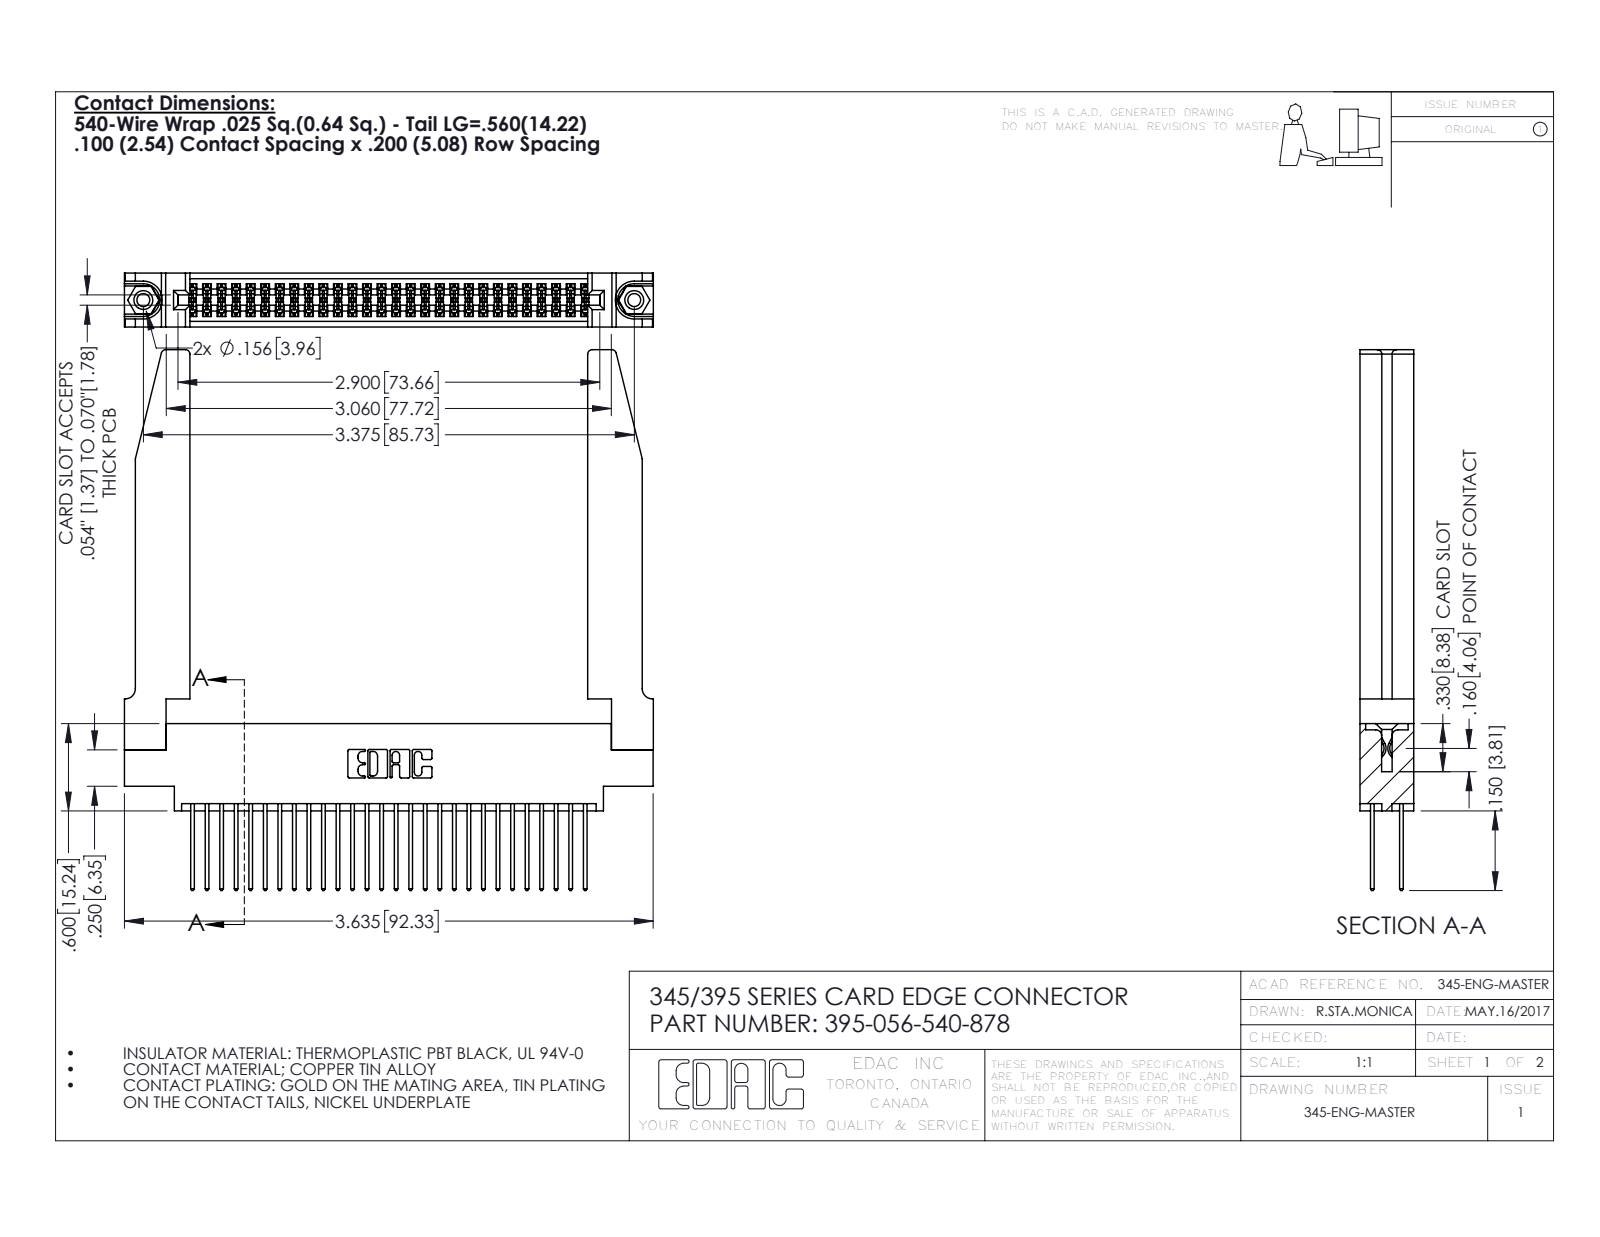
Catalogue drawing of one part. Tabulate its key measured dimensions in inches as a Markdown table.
| quantity | value |
| --- | --- |
| part name | 345-292-001_345-293-140; 395-056-540-878; 345-250-001_345-250-001-102; 345-220-078_345-220-078 (+1 more) |
| STEP written by | SolidWorks 2016 (CONFIG_CONTROL_DESIGN) |
| units | inches |
| bodies | 61 solids, 3164 faces (2074 planar, 1038 cylindrical, 52 other) |
| overall size | 3.717 × 3.636 × 0.37 |
| volume | 1.02 in³ |
| surface area | 32.41 in² |
| round holes (diameter × count) | 0.089 × 2, 0.125 × 2, 0.156 × 2, 0.064 × 1 |
| round bosses / shafts (diameter × count) | 0.155 × 2 |
| partial cylindrical surfaces (radius × count) | 0.006 × 84, 0.01 × 56, 0.01 × 22, 0.03 × 8, 0.007 × 6, 0.031 × 6, 0.026 × 3, 0.014 × 2 |
| main face-to-face distances | 0.37, 0.072, 0.298, 0.098, 0.272, 0.025, 0.2, 0.225, 0.175, 0.148 |
| hole center spacings | 0.27, 3.14, 3.375 |
